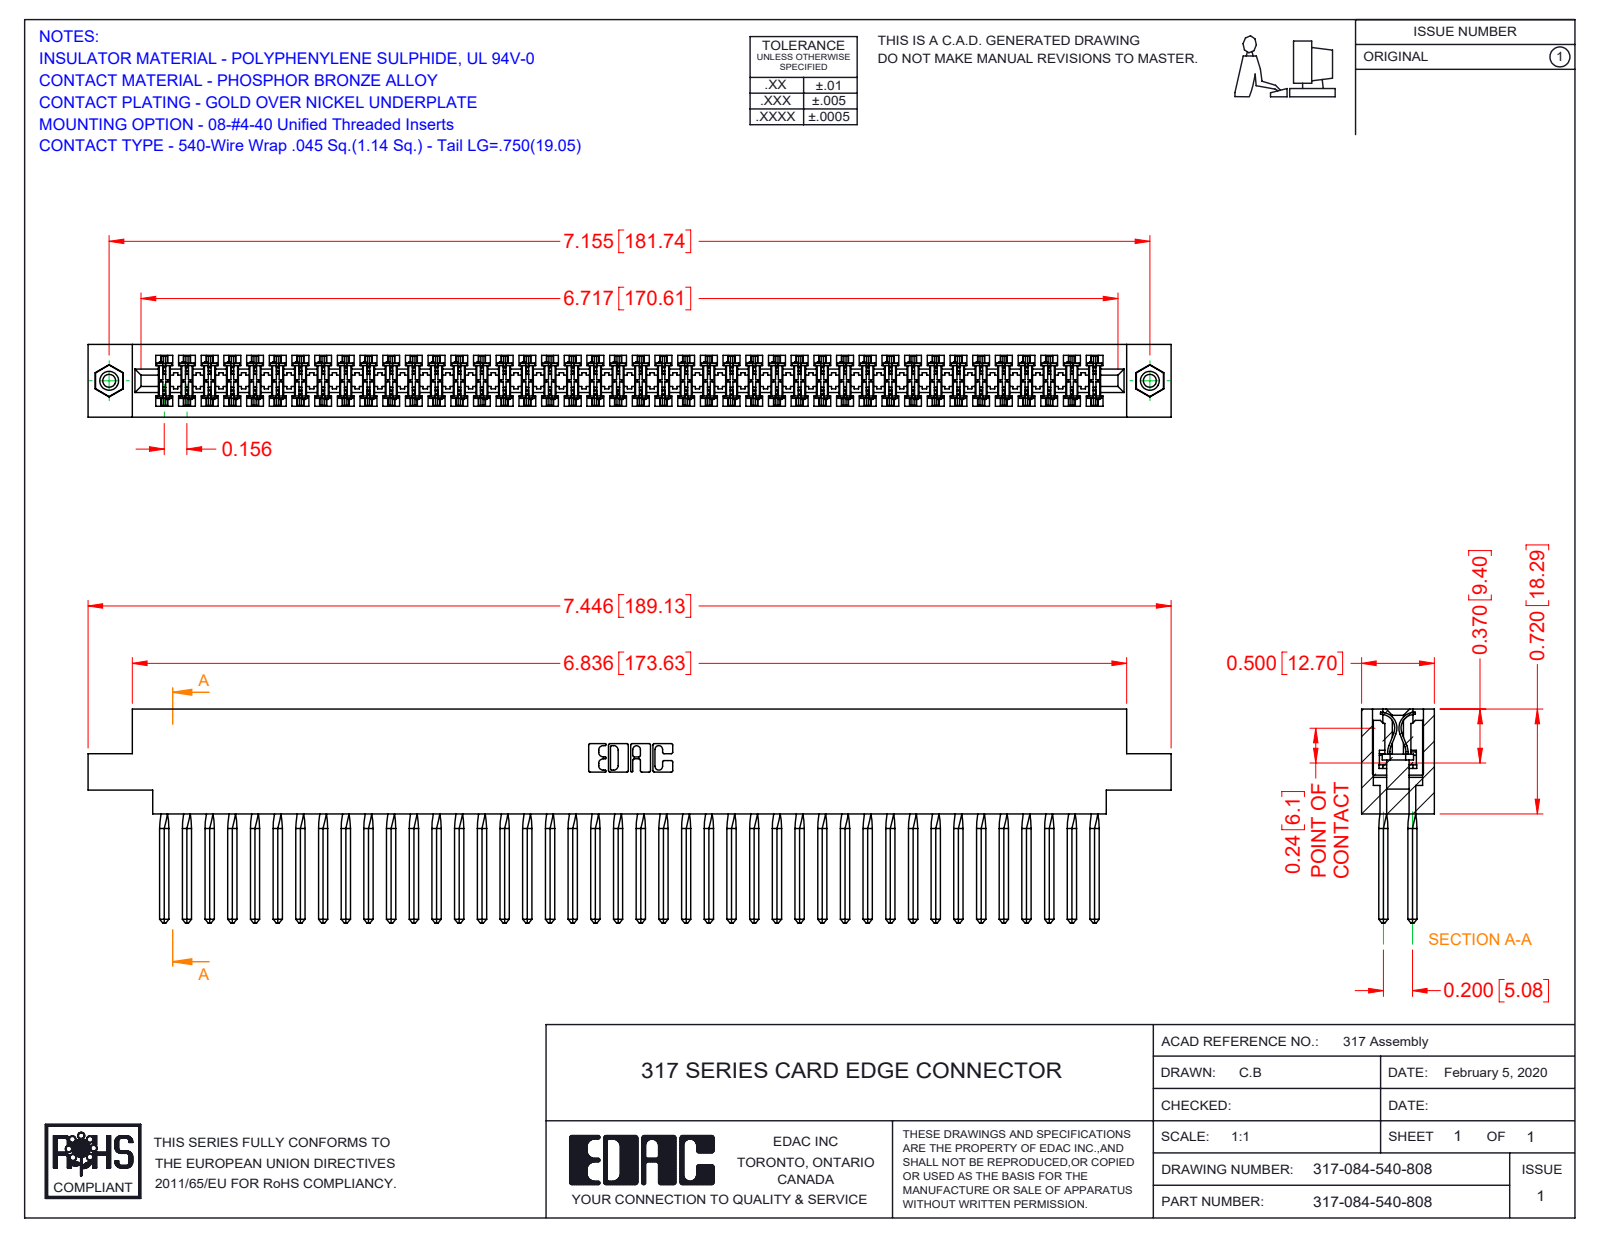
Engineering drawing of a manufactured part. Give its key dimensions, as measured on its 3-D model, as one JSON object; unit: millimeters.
{"part_name": "317-084-540-808; 345-250-001_345-250-003-102; 317 Part_.156 Dia - TI; 317-290-001_540", "step_written_by": "SolidWorks 2016 (CONFIG_CONTROL_DESIGN)", "units": "millimeters", "bodies": {"solids": 87, "faces": 7638, "planar": 6222, "cylindrical": 1064, "other": 352}, "overall_size": [189.1, 37.3, 12.7], "volume_mm3": 31740, "surface_area_mm2": 47340, "round_holes": [[2.3, 2], [3.2, 2], [4, 2]], "round_bosses_or_shafts": [[3.9, 2]], "partial_cylinders_radius": [[0.4, 168], [0.3, 22], [0.2, 6], [0.8, 6], [0.7, 3], [2.4, 2], [2.5, 2], [2.8, 2]], "face_to_face_distances": [12.7, 1.9, 10.8, 8.9, 5, 2.4, 5.1, 2.9, 3.3, 1.2], "hole_center_spacings": [181.7]}
